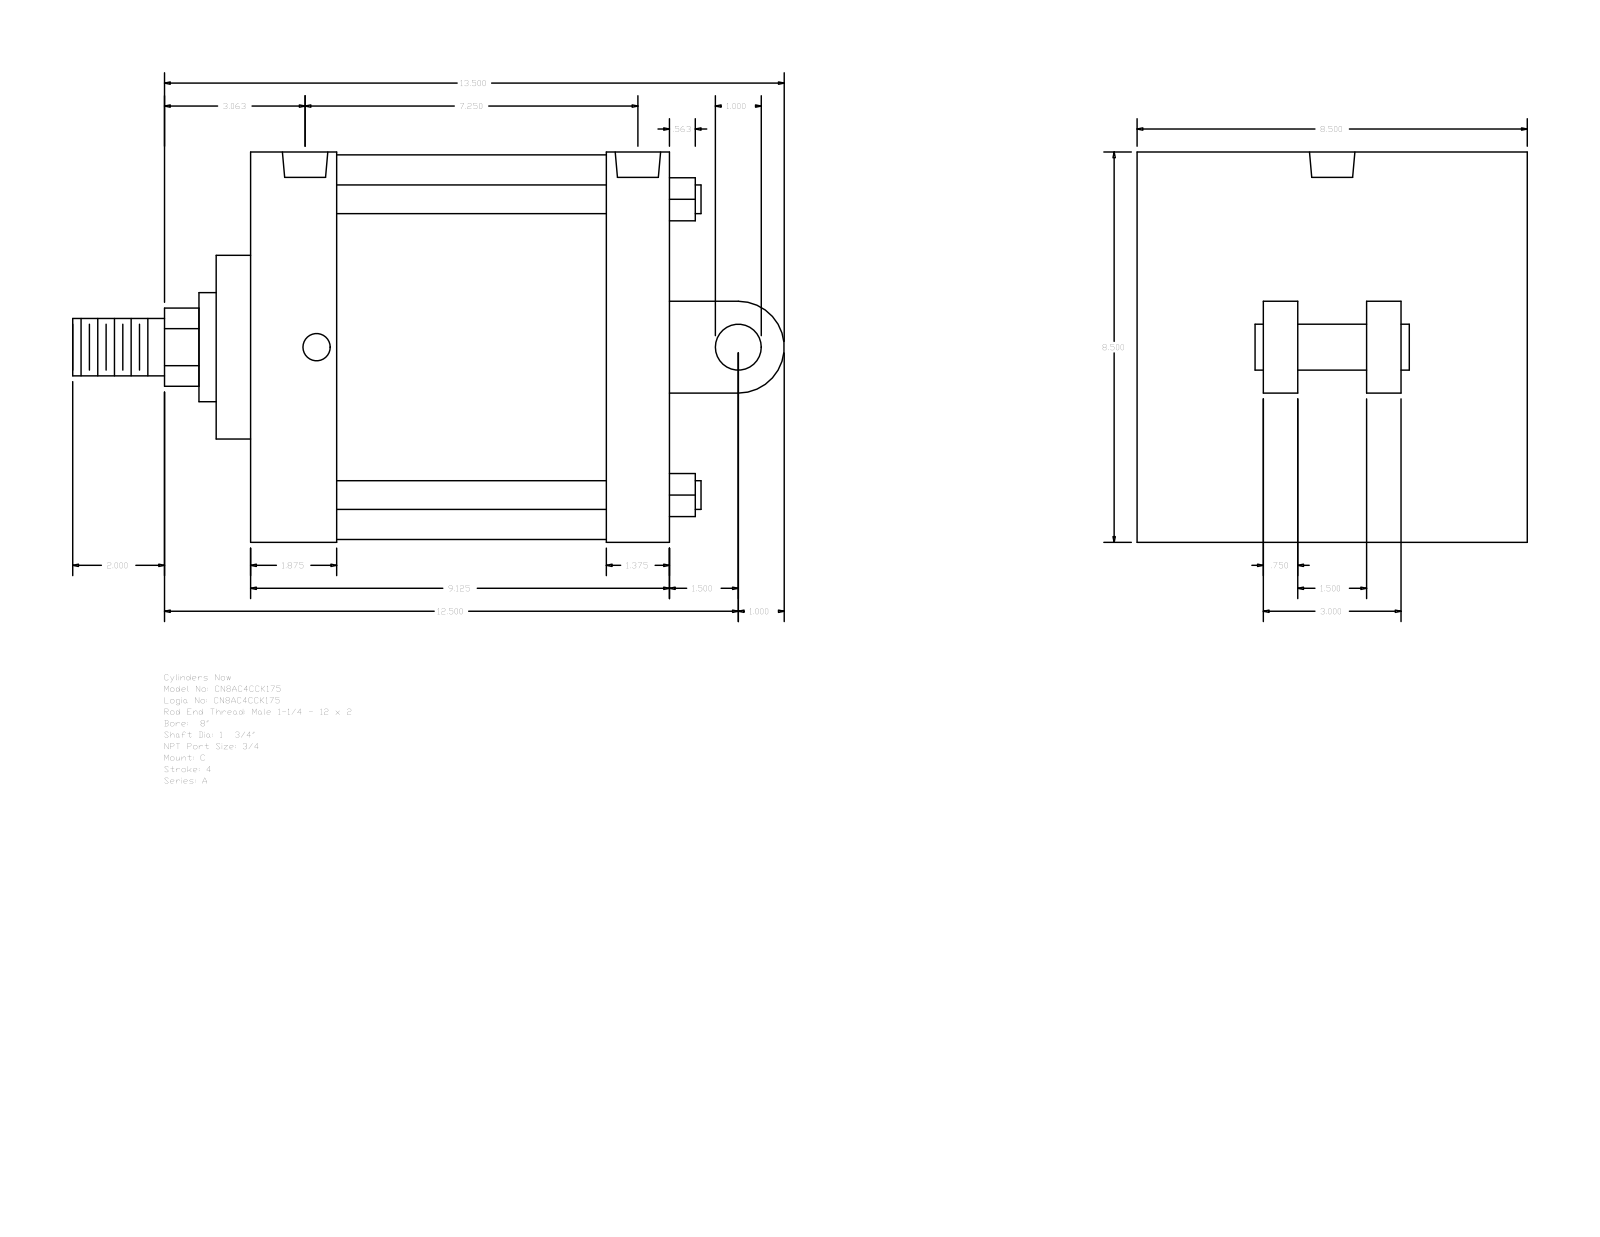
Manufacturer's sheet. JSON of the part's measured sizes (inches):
{"part_name": "A_C__0800_1.75", "step_written_by": "GSSL Pune (CONFIG_CONTROL_DESIGN)", "units": "inches", "bodies": {"solids": 0, "faces": 104, "planar": 75, "cylindrical": 29, "other": 0}, "overall_size": [15.5, 8.5, 8.5], "round_holes": [[0.594, 4], [0.989, 2]], "round_bosses_or_shafts": [[0.625, 4], [8.375, 1], [2.375, 1], [1.75, 1], [1.25, 1], [1, 1]], "partial_cylinders_radius": [[0.852, 1], [1, 1]], "face_to_face_distances": [8.5, 9.125, 0.75, 2.25, 5.875, 1.875, 7.25, 7.75, 1.375, 2.75], "hole_center_spacings": [0.25, 6.75, 7, 7.25]}
